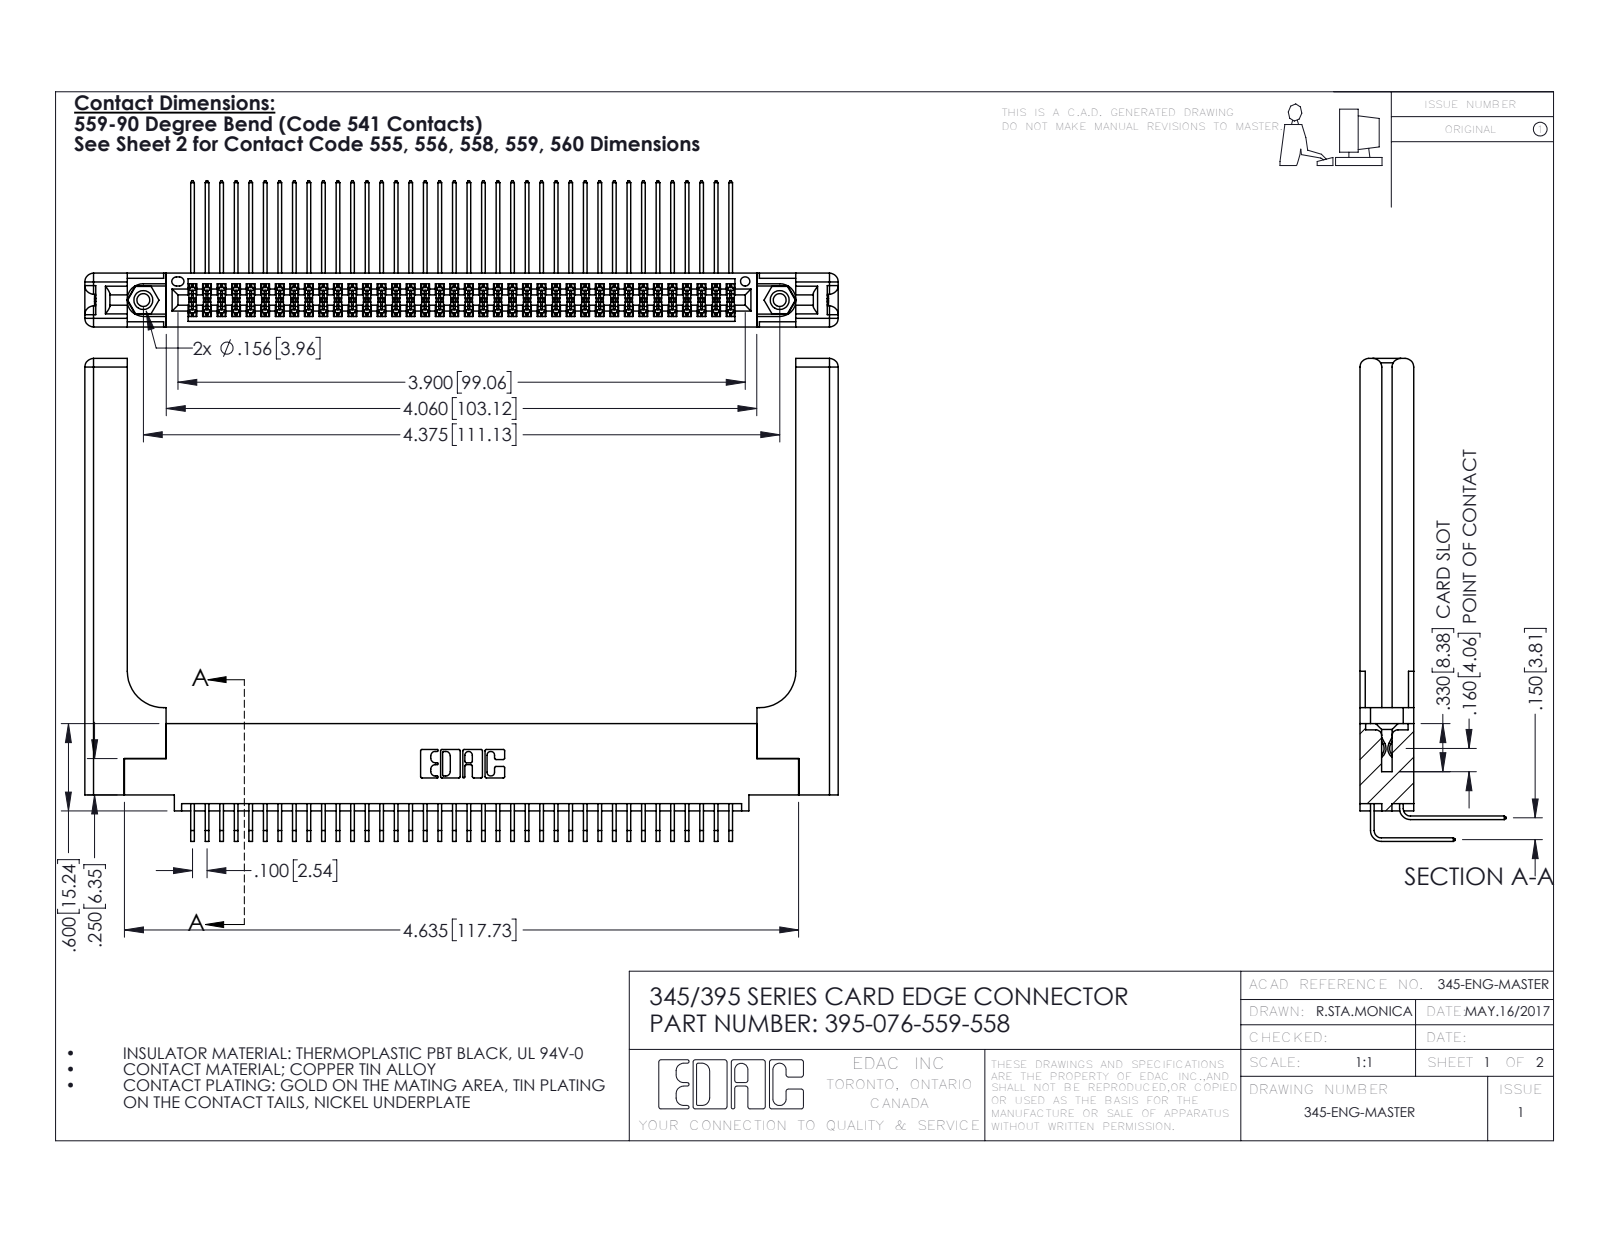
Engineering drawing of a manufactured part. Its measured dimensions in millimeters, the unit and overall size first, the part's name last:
Units: millimetres
Overall size (bounding box): 131.5 × 84.3 × 25.5
Round holes (diameter × count): ⌀2.3 ×2, ⌀3.2 ×2, ⌀4 ×2, ⌀1.6 ×1
Round bosses / shafts (diameter × count): ⌀3.9 ×2
Partial cylindrical surfaces — rounded edges, fillets, slot ends (radius × count): R0.2 ×115, R0.3 ×22, R1.5 ×16, R0.2 ×6, R0.8 ×6, R0.7 ×3, R0.4 ×2, R0.5 ×2
Main face-to-face distances: 1.8, 9.4, 7.6, 2.5, 6.9, 0.6, 5.1, 5.7, 3.8, 3.8
Hole centre spacings: 6.9, 105.1, 111.1
Volume: 21 580 mm³ · Surface area: 26 510 mm²
Bodies: 81 solids, 4338 faces (2892 planar, 1386 cylindrical, 60 other)
Part name (STEP PRODUCT): 345-220-058_345-220-058; 345 Part_0.110 Offset - 0.156 Dia-TH; 345-292-001_559 Tail - 2; 345-250-001_345-250-001-102 (+2 more)
STEP written by: SolidWorks 2016 (CONFIG_CONTROL_DESIGN)
